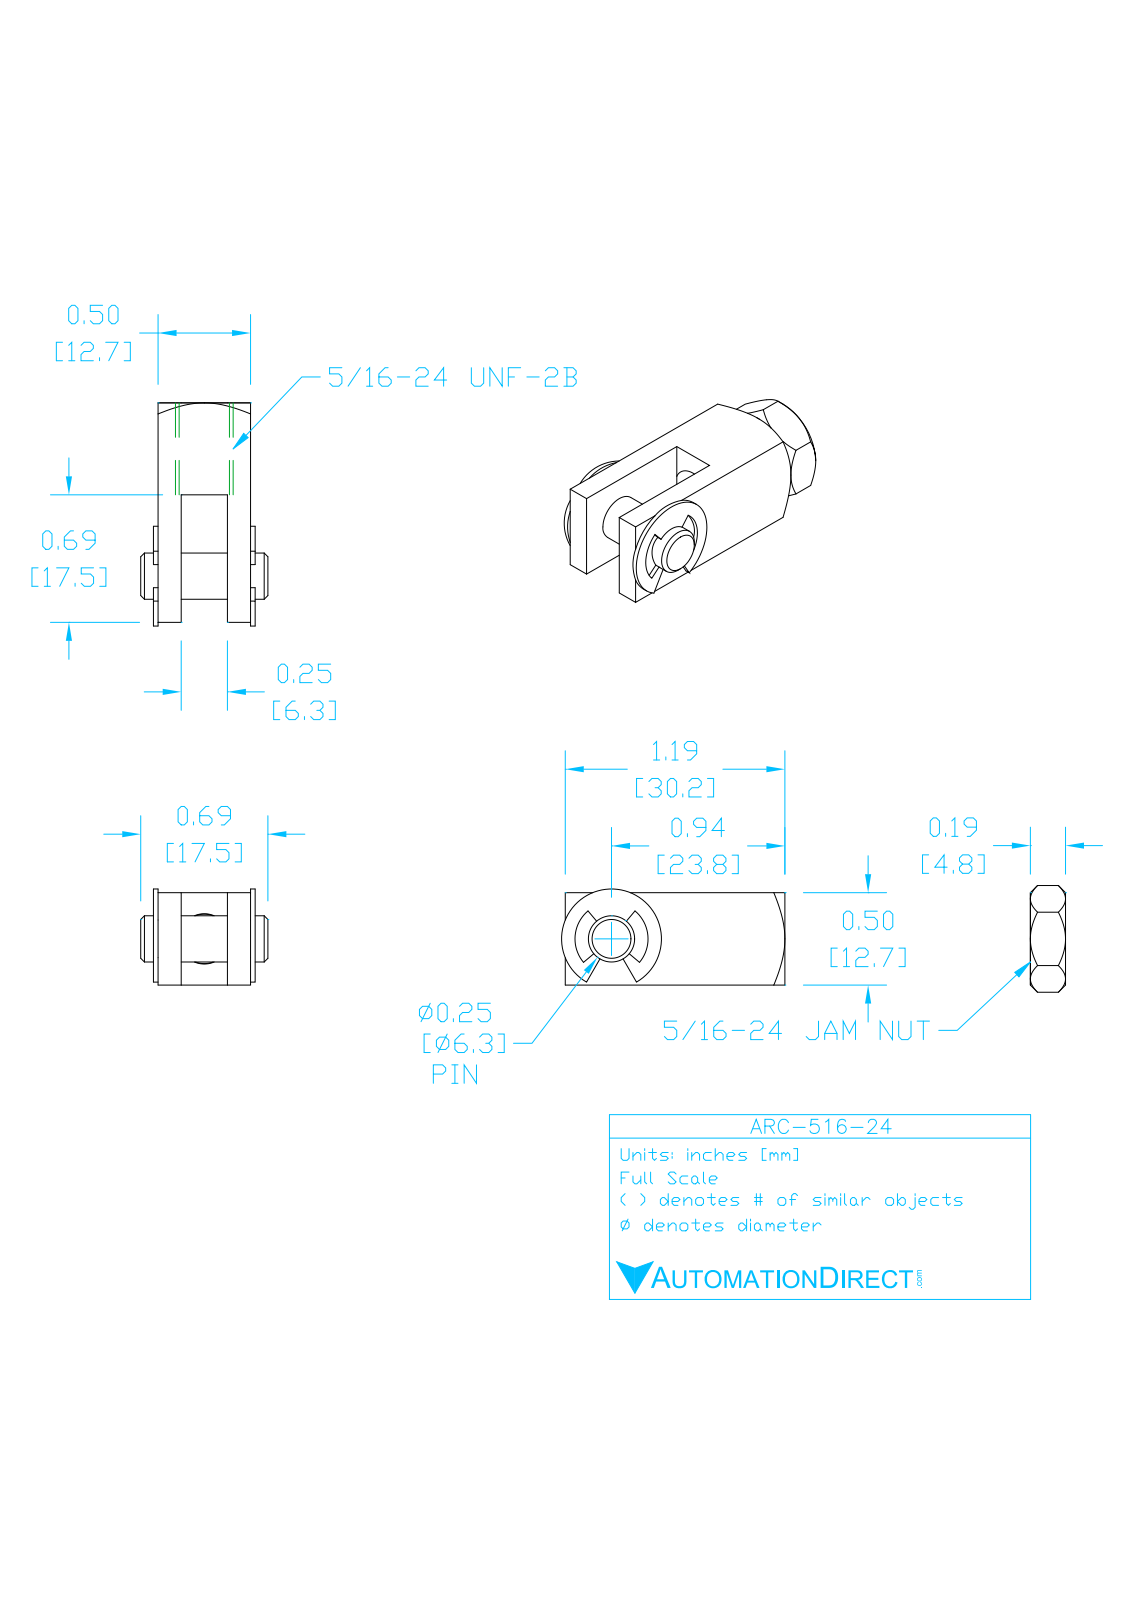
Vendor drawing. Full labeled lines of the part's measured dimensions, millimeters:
Part name (STEP PRODUCT): ARC-516-24
STEP written by: SolidWorks 2017 (AUTOMOTIVE_DESIGN)
Units: millimetres
Bodies: 5 solids, 140 faces (41 planar, 64 cylindrical, 35 other)
Overall size (bounding box): 34.2 × 17.5 × 12.9
Volume: 3 900 mm³ · Surface area: 3 425 mm²
Round holes (diameter × count): ⌀5.4 ×1, ⌀5.4 ×1, ⌀6.4 ×1
Round bosses / shafts (diameter × count): ⌀6.4 ×1, ⌀5.3 ×1
Partial cylindrical surfaces — rounded edges, fillets, slot ends (radius × count): R0.5 ×6, R0.6 ×4, R0.9 ×2, R2.7 ×1, R4.5 ×1, R6.4 ×1
Main face-to-face distances: 12.7, 3, 9.7, 6.7, 1.2, 13.9, 4.2, 10.8, 13.9, 3.1
